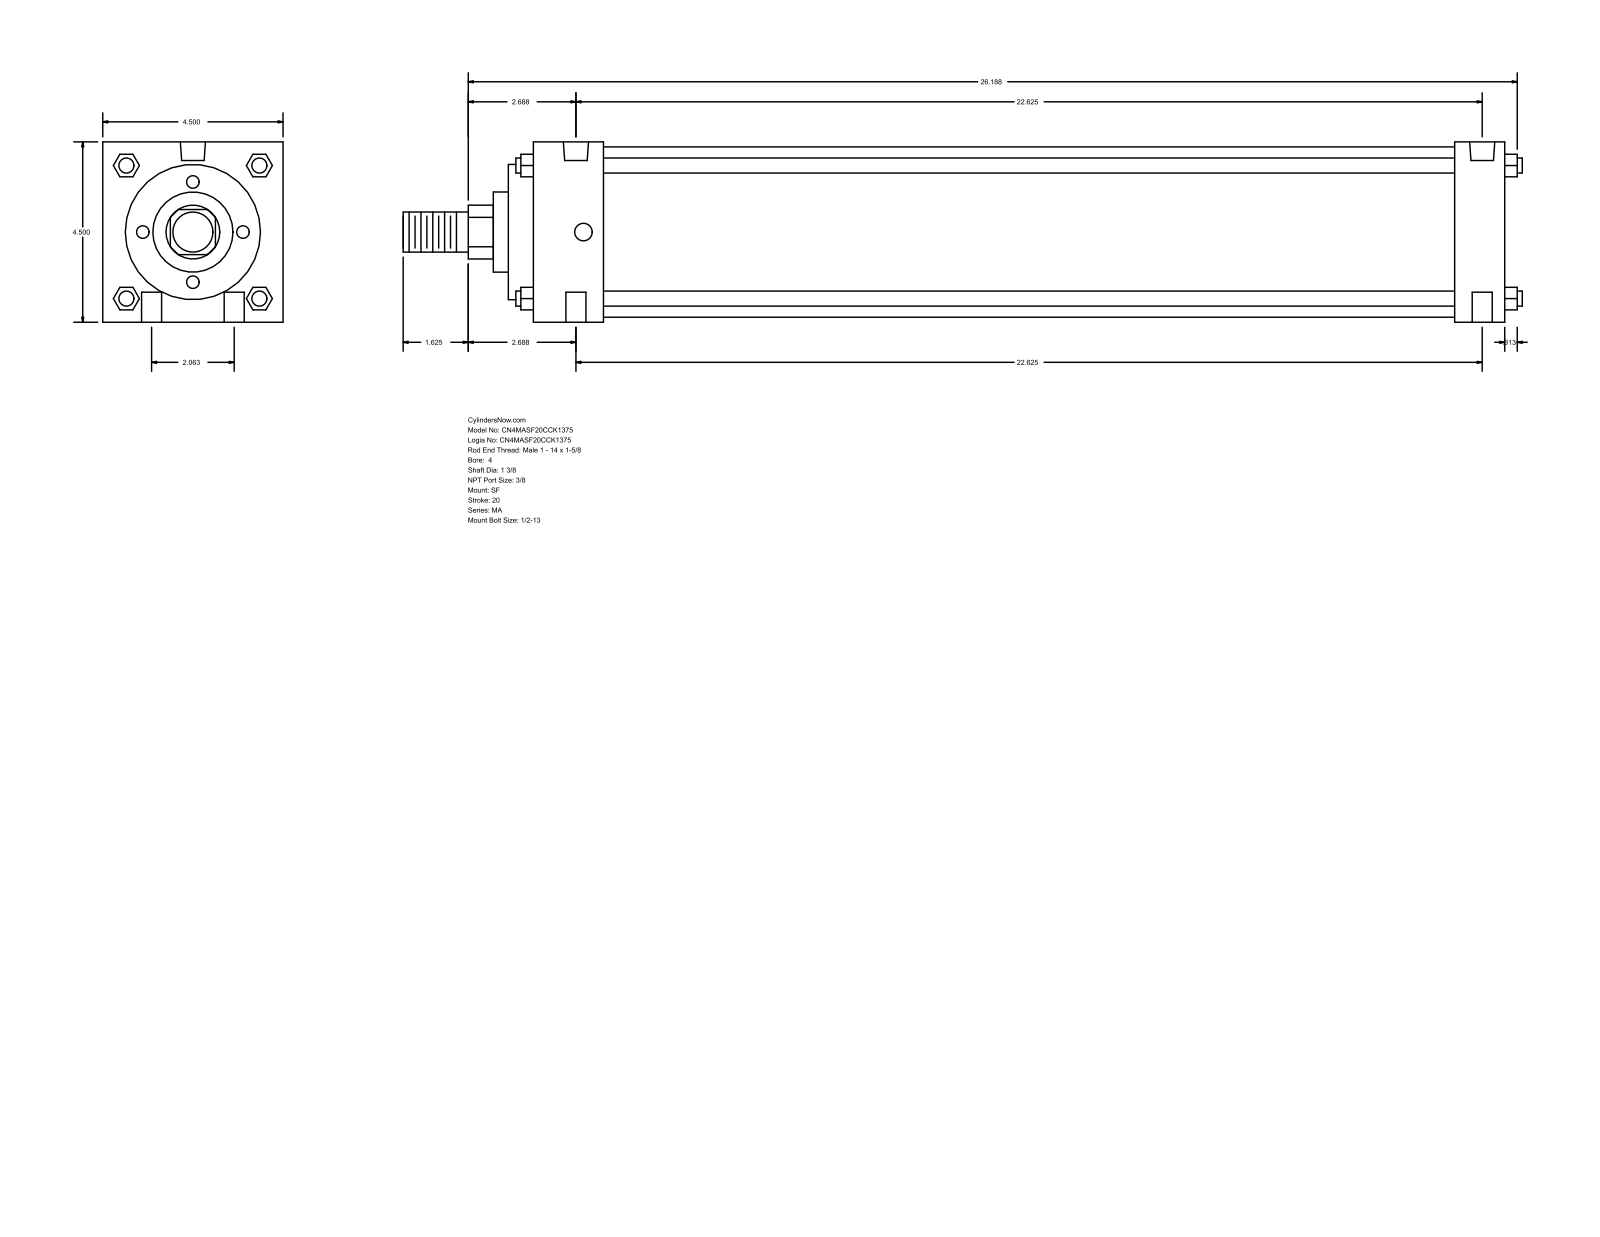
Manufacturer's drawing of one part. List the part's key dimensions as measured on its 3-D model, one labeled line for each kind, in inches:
Part name (STEP PRODUCT): MA_SF__0400_1.375
STEP written by: GSSL Pune (CONFIG_CONTROL_DESIGN)
Units: inches
Bodies: 0 solids, 126 faces (95 planar, 31 cylindrical, 0 other)
Overall size (bounding box): 27.937 × 4.5 × 4.5
Round holes (diameter × count): ⌀0.5 ×4, ⌀0.437 ×2, ⌀0.627 ×2
Round bosses / shafts (diameter × count): ⌀0.375 ×4, ⌀4.25 ×1, ⌀3.375 ×1, ⌀2 ×1, ⌀1.375 ×1, ⌀1 ×1
Partial cylindrical surfaces — rounded edges, fillets, slot ends (radius × count): R0.672 ×1
Main face-to-face distances: 4.5, 24.25, 0.625, 24.875, 23.625, 23, 1.25, 2.375, 1.75, 21.25
Hole centre spacings: 1.031, 22.649, 22.625, 2.062, 22.719, 22.25
